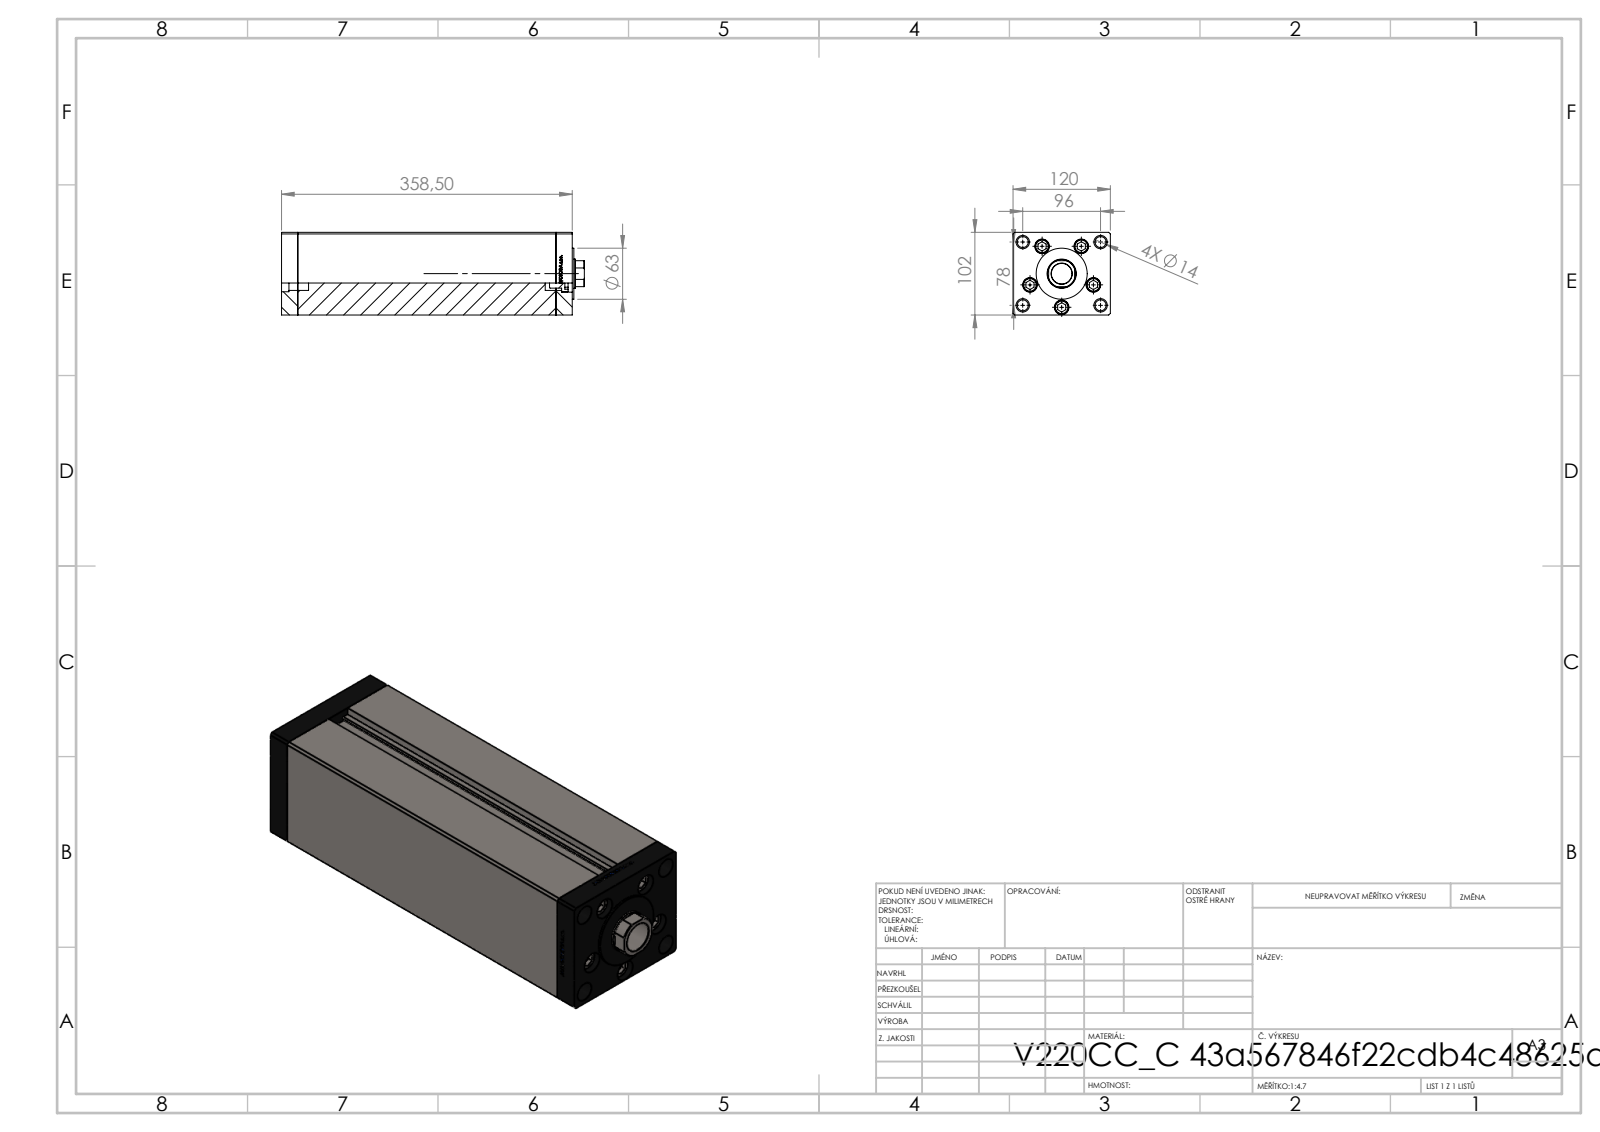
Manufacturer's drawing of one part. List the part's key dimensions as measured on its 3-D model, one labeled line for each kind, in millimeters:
Part name (STEP PRODUCT): V220C FRONT; V220C_VC_C; V220C BACK_C; V220C_C MIDDLE (+1 more)
STEP written by: SolidWorks 2019 (CONFIG_CONTROL_DESIGN)
Units: millimetres
Bodies: 13 solids, 1165 faces (542 planar, 161 cylindrical, 462 other)
Overall size (bounding box): 373.5 × 120 × 102
Volume: 3 632 000 mm³ · Surface area: 414 640 mm²
Round holes (diameter × count): ⌀13.5 ×9, ⌀18 ×5, ⌀12 ×4, ⌀16.5 ×4, ⌀17 ×1, ⌀25.5 ×1, ⌀36 ×1
Round bosses / shafts (diameter × count): ⌀8 ×5, ⌀17 ×4, ⌀63 ×1
Partial cylindrical surfaces — rounded edges, fillets, slot ends (radius × count): R0.93 ×2, R17.5 ×1
Main face-to-face distances: 120, 102, 20, 318.5, 338.5, 34.25, 358.5, 324.25, 304.25, 14.25
Hole centre spacings: 41.5, 61.85, 24.39, 26.69, 47.92, 48.07, 49.84, 53.57
